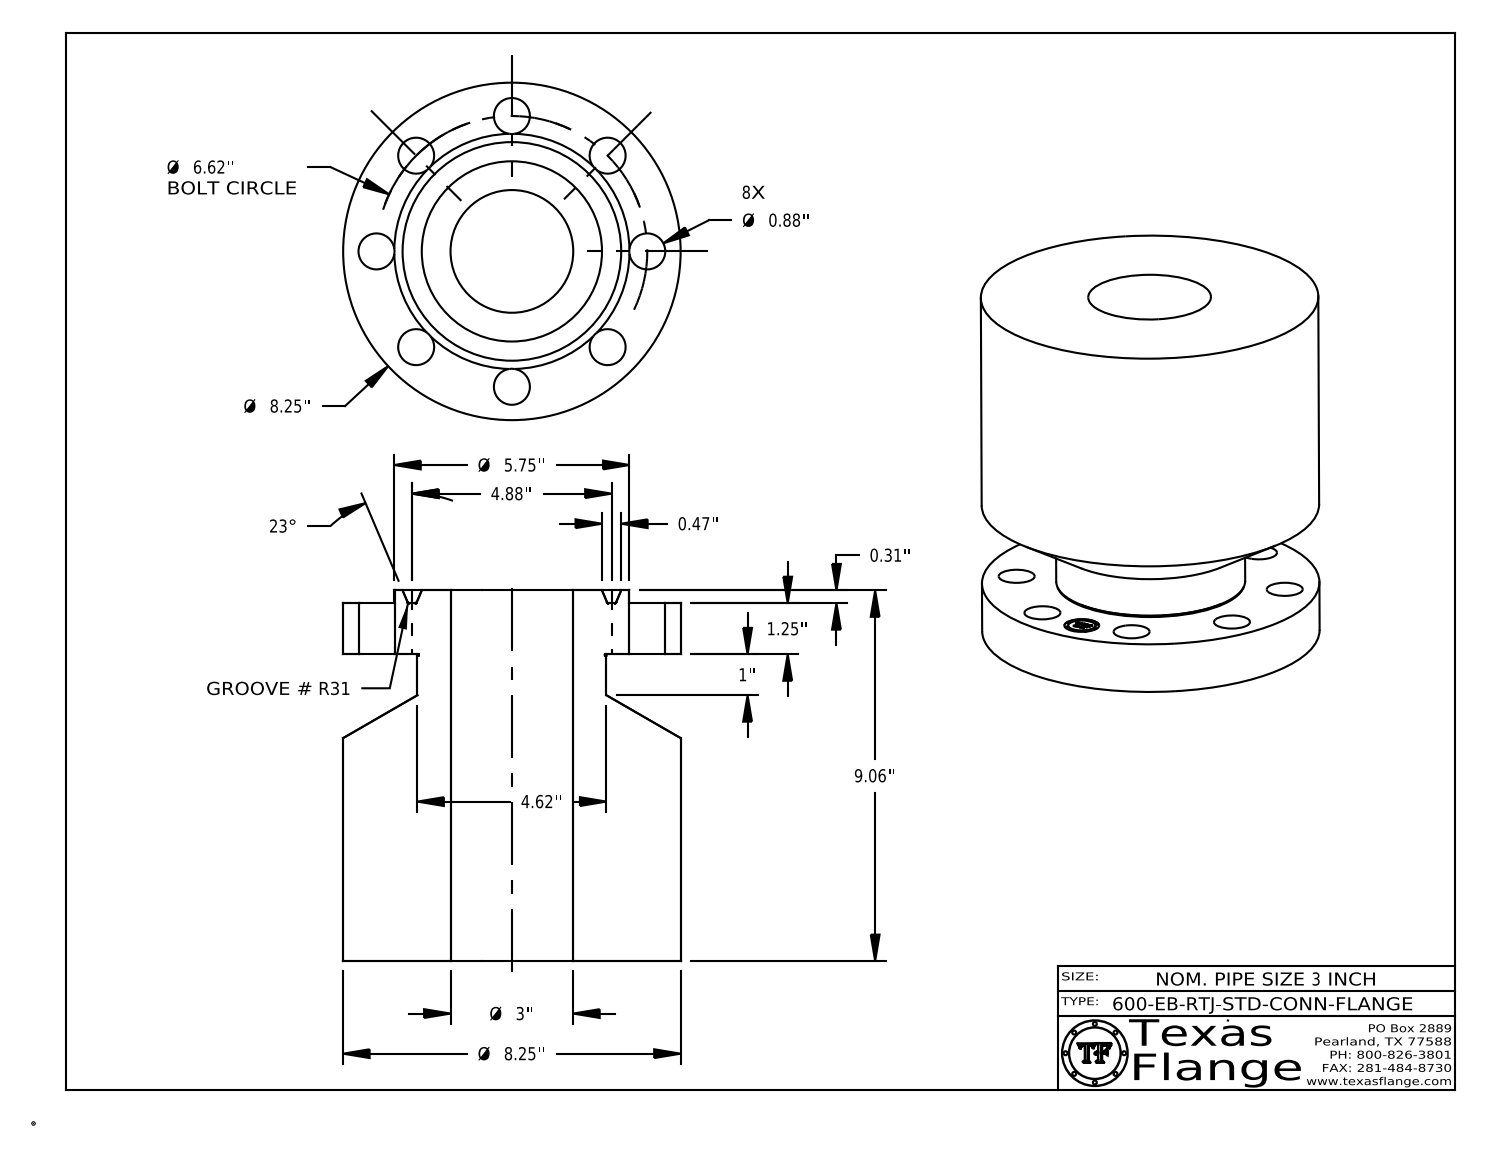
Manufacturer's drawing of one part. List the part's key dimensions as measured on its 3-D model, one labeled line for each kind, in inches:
Part name (STEP PRODUCT): 3-600-EB-RTJ-STD-CONN-FLANGE
STEP written by: CATIA V5 STEP AP214 (AUTOMOTIVE_DESIGN)
Units: inches
Bodies: 1 solid, 439 faces (371 planar, 54 cylindrical, 14 other)
Overall size (bounding box): 9.063 × 8.25 × 8.25
Volume: 346.4 in³ · Surface area: 475.9 in²
Round holes (diameter × count): ⌀0.88 ×8, ⌀0.85 ×1, ⌀3 ×1
Round bosses / shafts (diameter × count): ⌀0.051 ×8, ⌀8.25 ×1, ⌀5.75 ×1, ⌀4.62 ×1, ⌀0.67 ×1
Main face-to-face distances: 7.5, 1.25, 8.75, 0.313, 1.563, 9.063, 1.558, 1.245, 7.505, 0.016
Hole centre spacings: 3.31, 2.533, 6.116, 4.681, 4.681, 1.291, 3.678, 6.493
